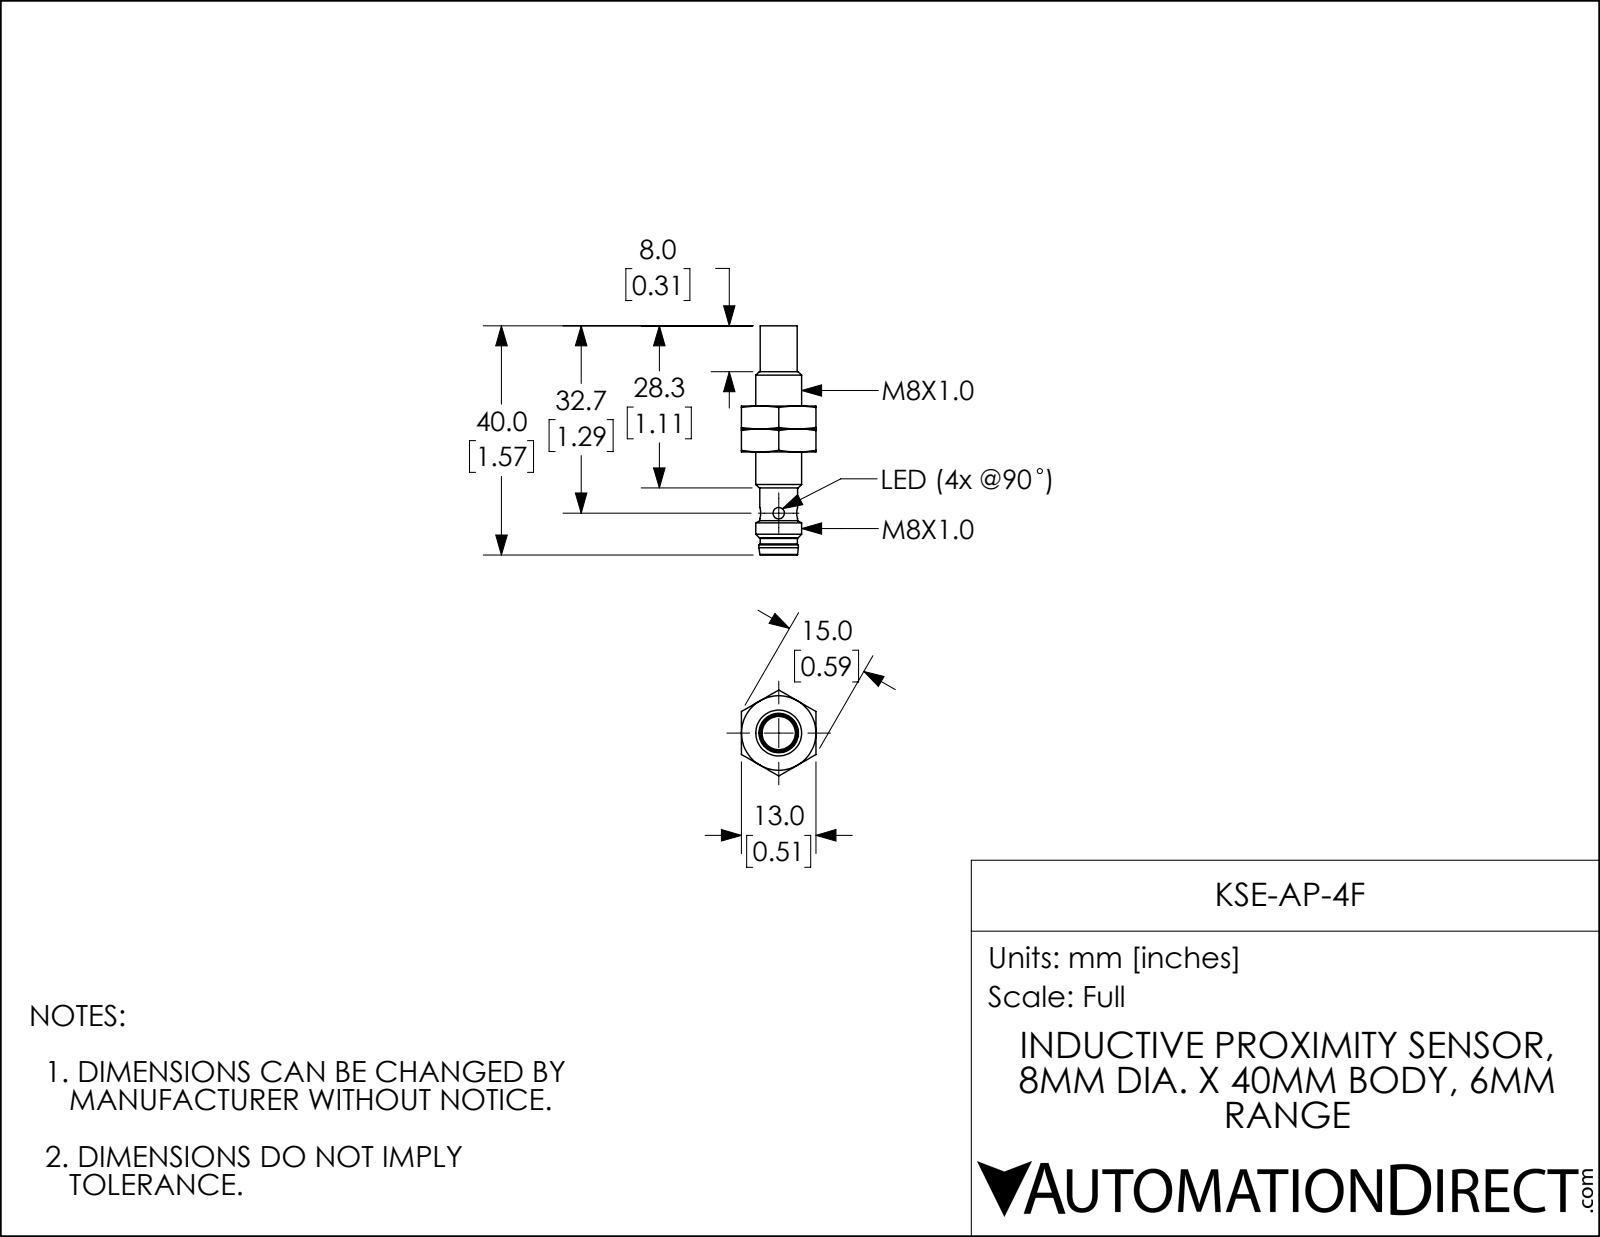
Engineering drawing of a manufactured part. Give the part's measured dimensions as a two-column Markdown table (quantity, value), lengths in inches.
| quantity | value |
| --- | --- |
| part name | KSE-AP-4F |
| STEP written by | SolidWorks 2017 (AUTOMOTIVE_DESIGN) |
| units | inches |
| bodies | 3 solids, 77 faces (22 planar, 14 cylindrical, 41 other) |
| overall size | 1.575 × 0.591 × 0.512 |
| volume | 0.148 in³ |
| surface area | 3.188 in² |
| round holes (diameter × count) | 0.228 × 1, 0.272 × 1 |
| round bosses / shafts (diameter × count) | 0.315 × 1, 0.272 × 1, 0.26 × 1, 0.256 × 1, 0.254 × 1, 0.25 × 1 |
| partial cylindrical surfaces (radius × count) | 0.13 × 4 |
| main face-to-face distances | 0.512, 0.157, 0.315, 0.551, 0.709, 0.866, 0.51, 0.667, 0.825, 1.376 |
